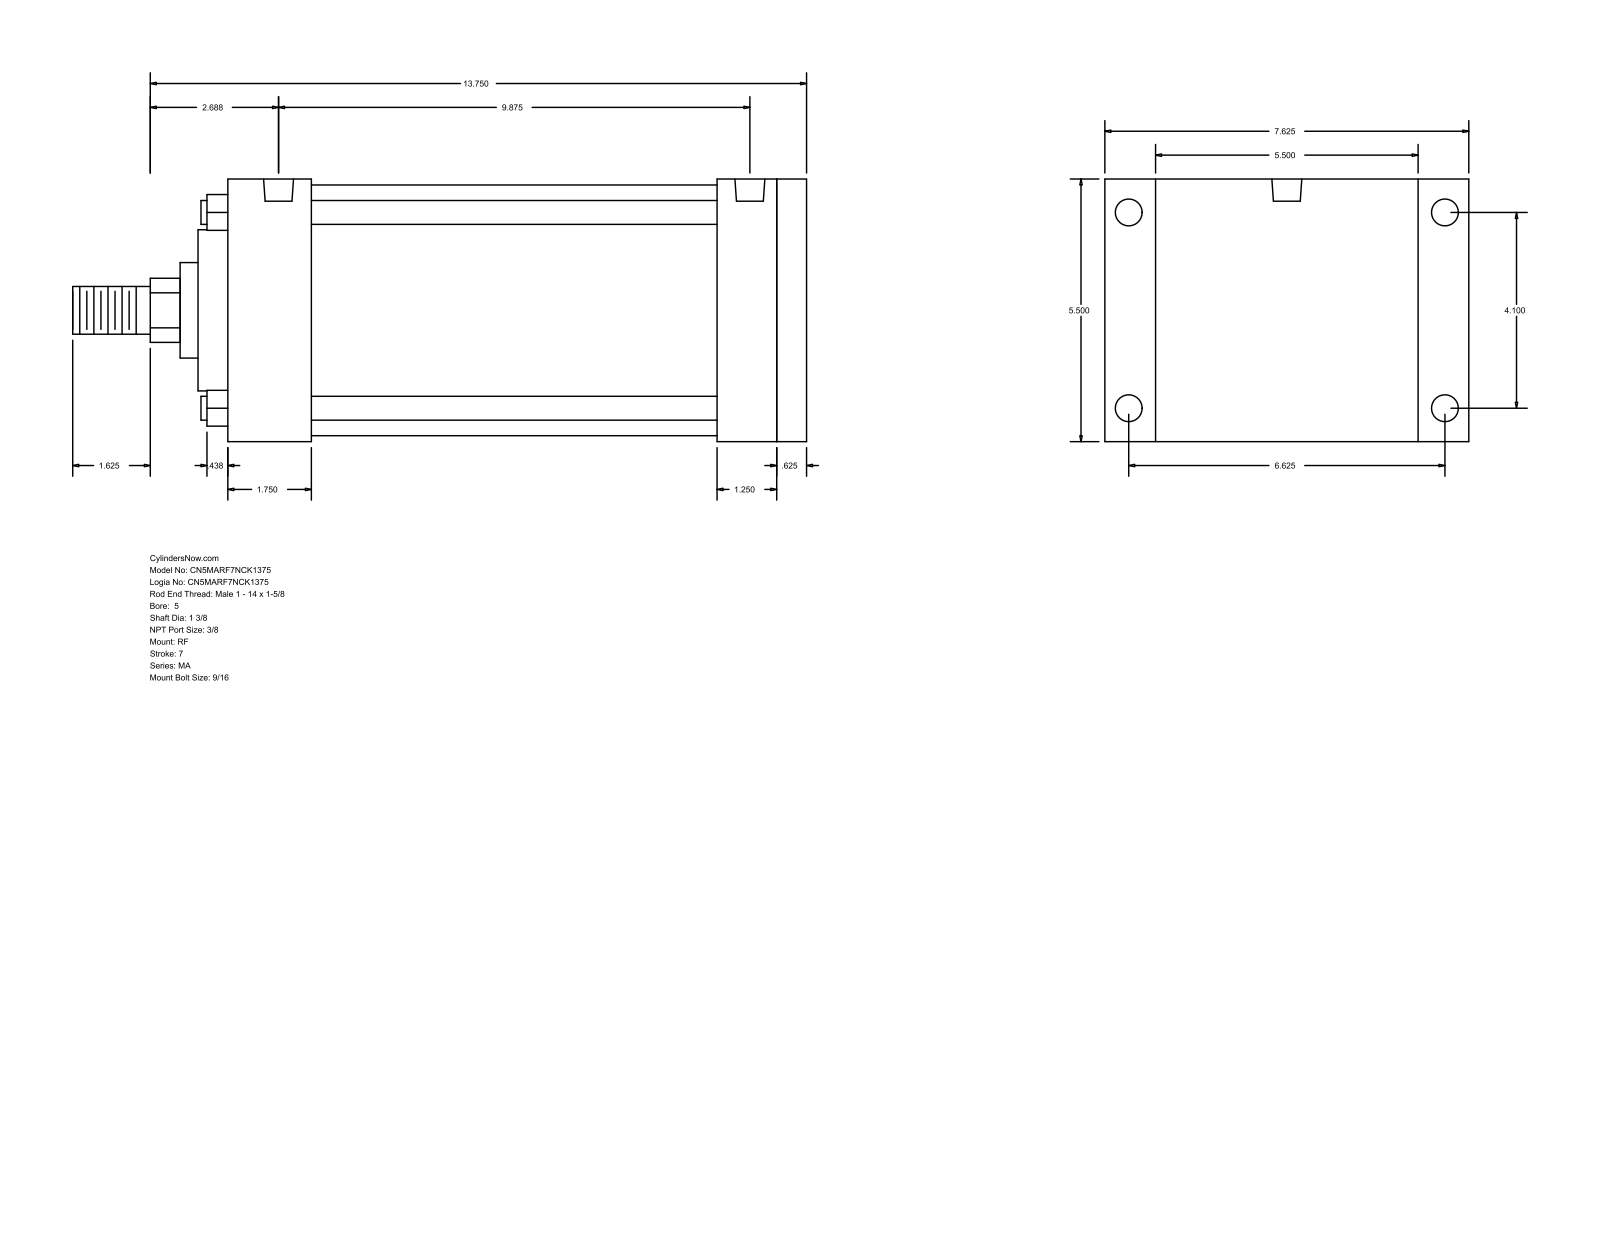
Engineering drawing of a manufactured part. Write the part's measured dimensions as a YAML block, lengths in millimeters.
part_name: "MA_RF__0500_1.375"
step_written_by: "GSSL Pune (CONFIG_CONTROL_DESIGN)"
units: millimeters
bodies: {solids: 0, faces: 94, planar: 65, cylindrical: 29, other: 0}
overall_size: [390.52, 193.68, 139.7]
round_holes:
  - {diameter: 11.11, count: 4}
  - {diameter: 14.29, count: 4}
  - {diameter: 15.93, count: 2}
round_bosses_or_shafts:
  - {diameter: 12.7, count: 4}
  - {diameter: 133.35, count: 1}
  - {diameter: 85.72, count: 1}
  - {diameter: 50.8, count: 1}
  - {diameter: 34.92, count: 1}
  - {diameter: 25.4, count: 1}
partial_cylinders:
  - {radius: 17.06, count: 1}
face_to_face_distances: [139.7, 307.98, 15.87, 292.11, 44.45, 247.66, 263.53, 260.35, 215.9, 31.76]
hole_center_spacings: [4.77, 104.14, 168.28, 197.9, 241.29, 246.06, 250.83]
